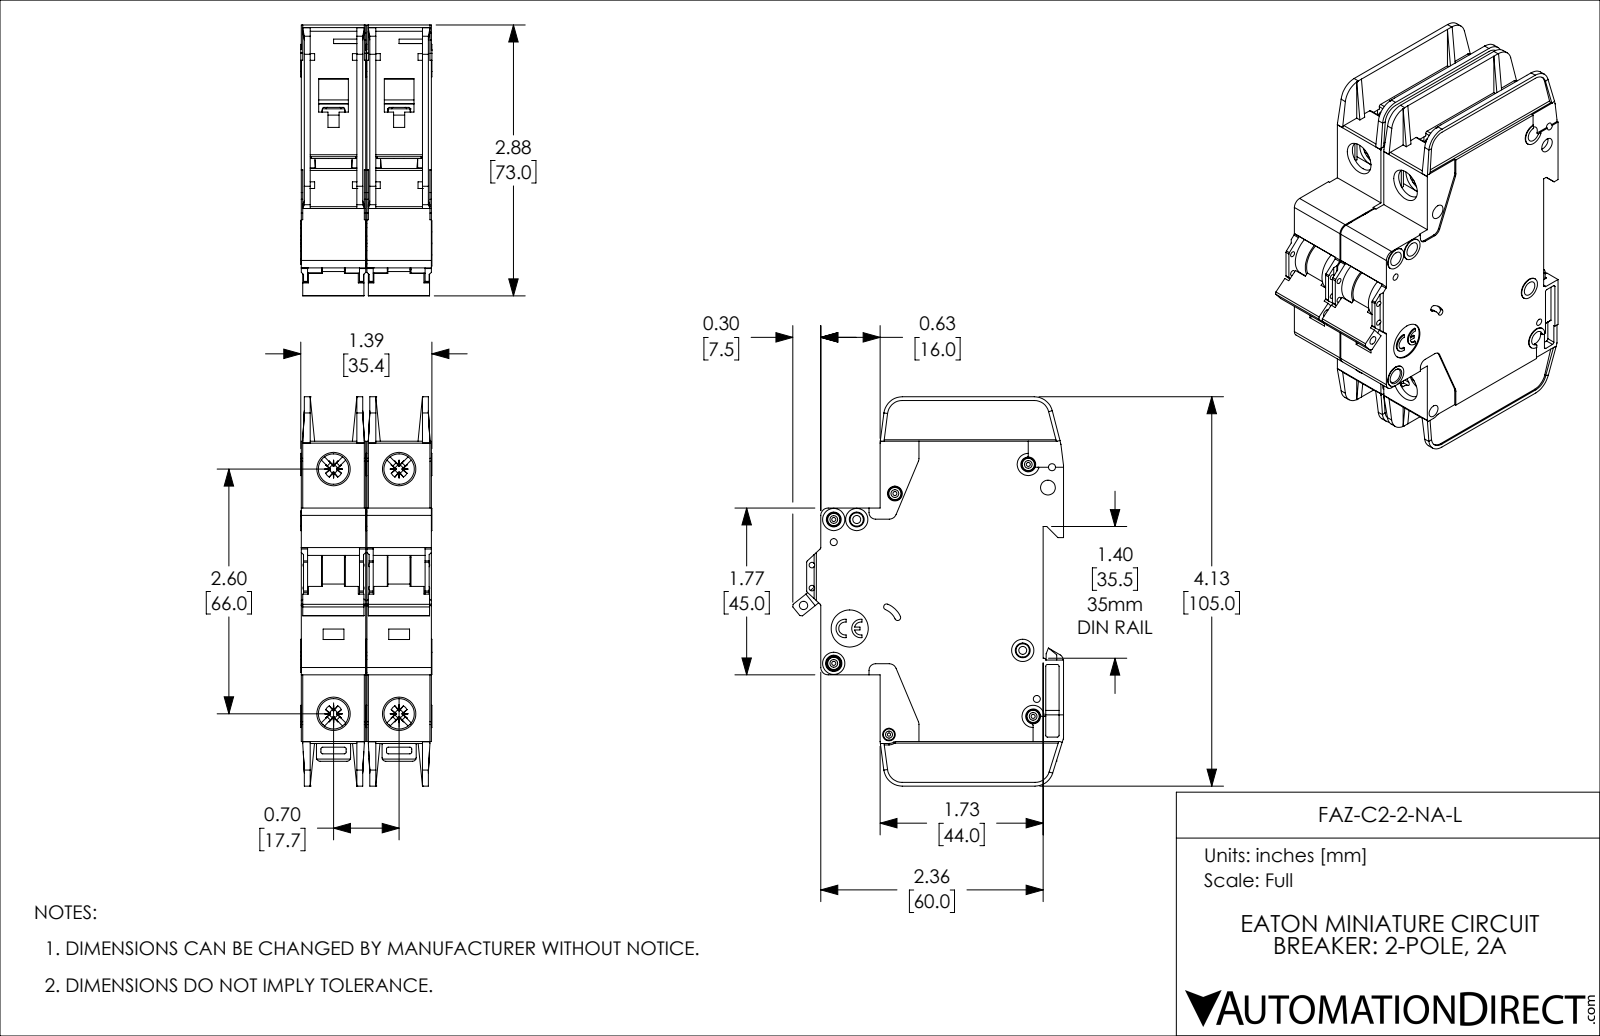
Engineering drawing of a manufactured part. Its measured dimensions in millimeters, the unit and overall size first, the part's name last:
Units: millimetres
Overall size (bounding box): 105 × 73.1 × 35.4
Round holes (diameter × count): ⌀4 ×8, ⌀1.1 ×5, ⌀1.9 ×4, ⌀8.2 ×4, ⌀1.5 ×2, ⌀2.2 ×2, ⌀0.9 ×1, ⌀2.3 ×1, ⌀2.5 ×1, ⌀3.4 ×1, ⌀10 ×1
Round bosses / shafts (diameter × count): ⌀3.3 ×5, ⌀6 ×4, ⌀3 ×3, ⌀2.5 ×2
Partial cylindrical surfaces — rounded edges, fillets, slot ends (radius × count): R0.5 ×57, R0.4 ×20, R1 ×14, R2 ×10, R1.1 ×8, R0.2 ×5, R5 ×5, R0.3 ×4
Main face-to-face distances: 17.7, 1.2, 17.4, 15, 2.4, 16.2, 13.8, 35.1, 18.9, 16.5
Hole centre spacings: 6.2, 13.6, 17.7, 22.1, 66, 68.3, 4.8, 5.1
Volume: 153 500 mm³ · Surface area: 52 910 mm²
Bodies: 2 solids, 2254 faces (1342 planar, 714 cylindrical, 198 other)
Part name (STEP PRODUCT): FAZ-C2-2-NA-L
STEP written by: SolidWorks 2019 (AUTOMOTIVE_DESIGN)
